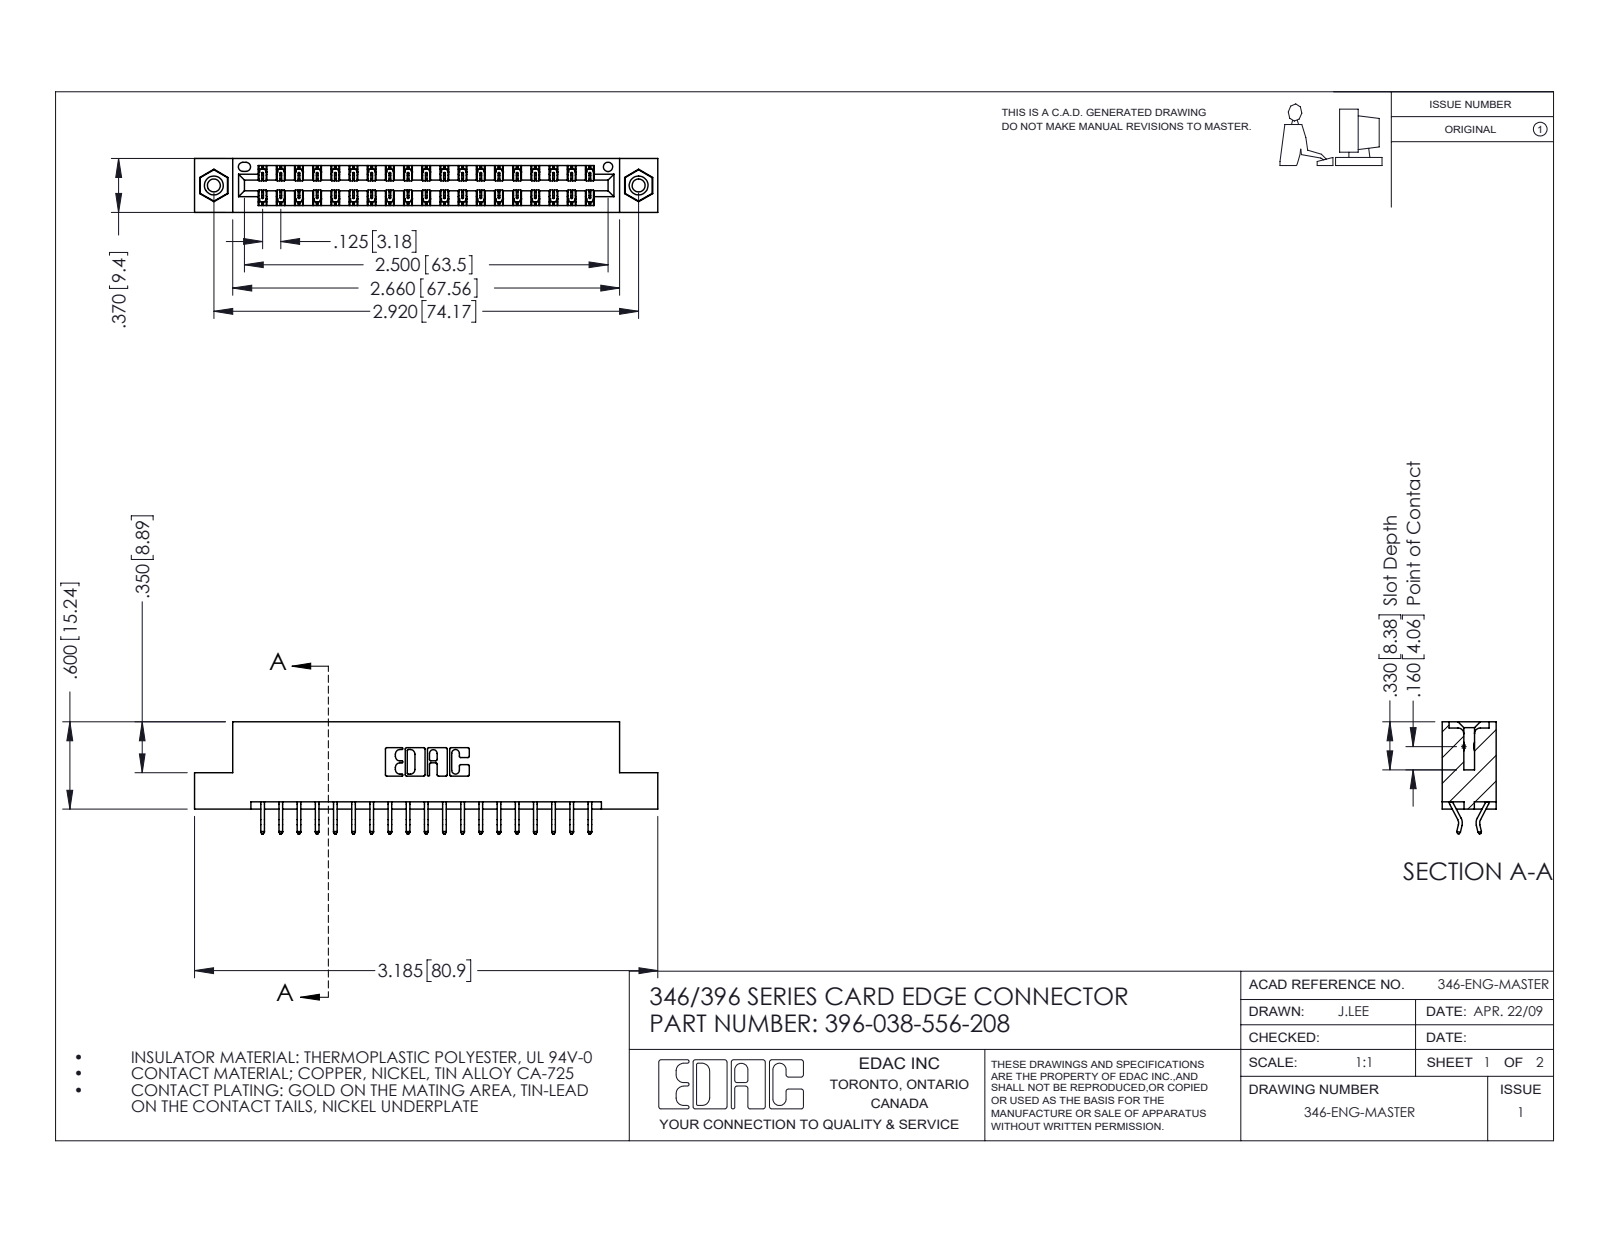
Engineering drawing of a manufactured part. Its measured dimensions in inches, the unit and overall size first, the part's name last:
Units: inches
Overall size (bounding box): 3.185 × 0.77 × 0.37
Round holes (diameter × count): ⌀0.089 ×2, ⌀0.125 ×2, ⌀0.156 ×2, ⌀0.064 ×1
Round bosses / shafts (diameter × count): ⌀0.155 ×2
Partial cylindrical surfaces — rounded edges, fillets, slot ends (radius × count): R0.006 ×57, R0.01 ×22, R0.007 ×6, R0.031 ×6, R0.026 ×3, R0.01 ×2, R0.014 ×2, R0.022 ×2
Main face-to-face distances: 0.048, 0.322, 0.37, 0.25, 0.025, 0.072, 0.298, 0.275, 0.148, 0.222
Hole centre spacings: 0.246, 2.713, 2.92
Volume: 0.47 in³ · Surface area: 15.83 in²
Bodies: 41 solids, 2386 faces (1590 planar, 780 cylindrical, 16 other)
Part name (STEP PRODUCT): 345-292-001_556 Tail; 345-250-001_345-250-003-102; 396-038-556-208; 346 Part_Flush Mounting Lugs - 0.156 Dia-TI
STEP written by: SolidWorks 2016 (CONFIG_CONTROL_DESIGN)
